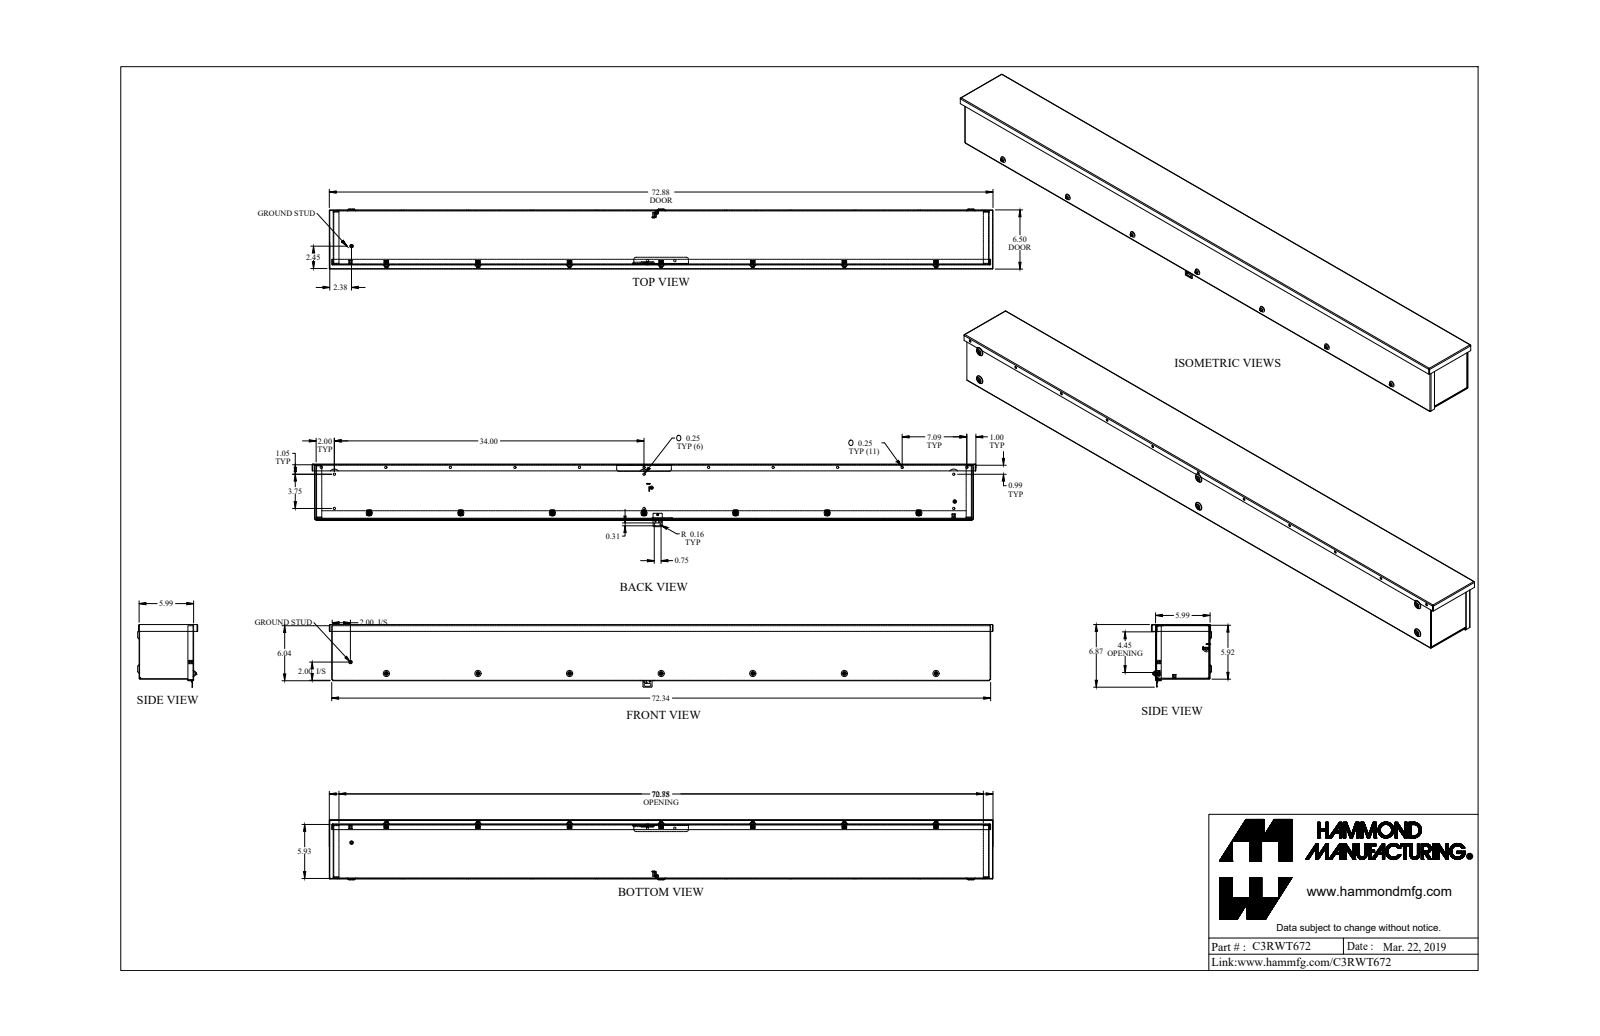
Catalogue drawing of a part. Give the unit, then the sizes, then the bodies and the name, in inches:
Units: inches
Overall size (bounding box): 72.875 × 6.871 × 6.594
Round holes (diameter × count): ⌀0.25 ×19, ⌀0.156 ×9, ⌀0.214 ×7, ⌀0.23 ×7, ⌀0.203 ×2, ⌀0.125 ×1, ⌀0.137 ×1, ⌀0.2 ×1, ⌀0.215 ×1
Round bosses / shafts (diameter × count): ⌀0.19 ×8, ⌀0.148 ×7, ⌀0.375 ×2, ⌀0.5 ×1, ⌀0.367 ×1, ⌀0.21 ×1, ⌀0.152 ×1, ⌀0.125 ×1
Partial cylindrical surfaces — rounded edges, fillets, slot ends (radius × count): R0.08 ×28, R0.108 ×28, R0.125 ×17, R0.022 ×14, R0.029 ×14, R0.086 ×14, R0.171 ×7, R0.206 ×7
Main face-to-face distances: 0.057, 5.928, 0.057, 5.871, 5.985, 5.886, 5.943, 6, 5.943, 0.114
Hole centre spacings: 7.087, 28.35, 21.263, 14.175, 35.437, 10.057, 14.175, 20.115
Volume: 118.7 in³ · Surface area: 4 203 in²
Bodies: 35 solids, 1323 faces (712 planar, 423 cylindrical, 188 other)
Part name (STEP PRODUCT): C3RWT672_Default
STEP written by: SolidWorks 2019 (CONFIG_CONTROL_DESIGN)
